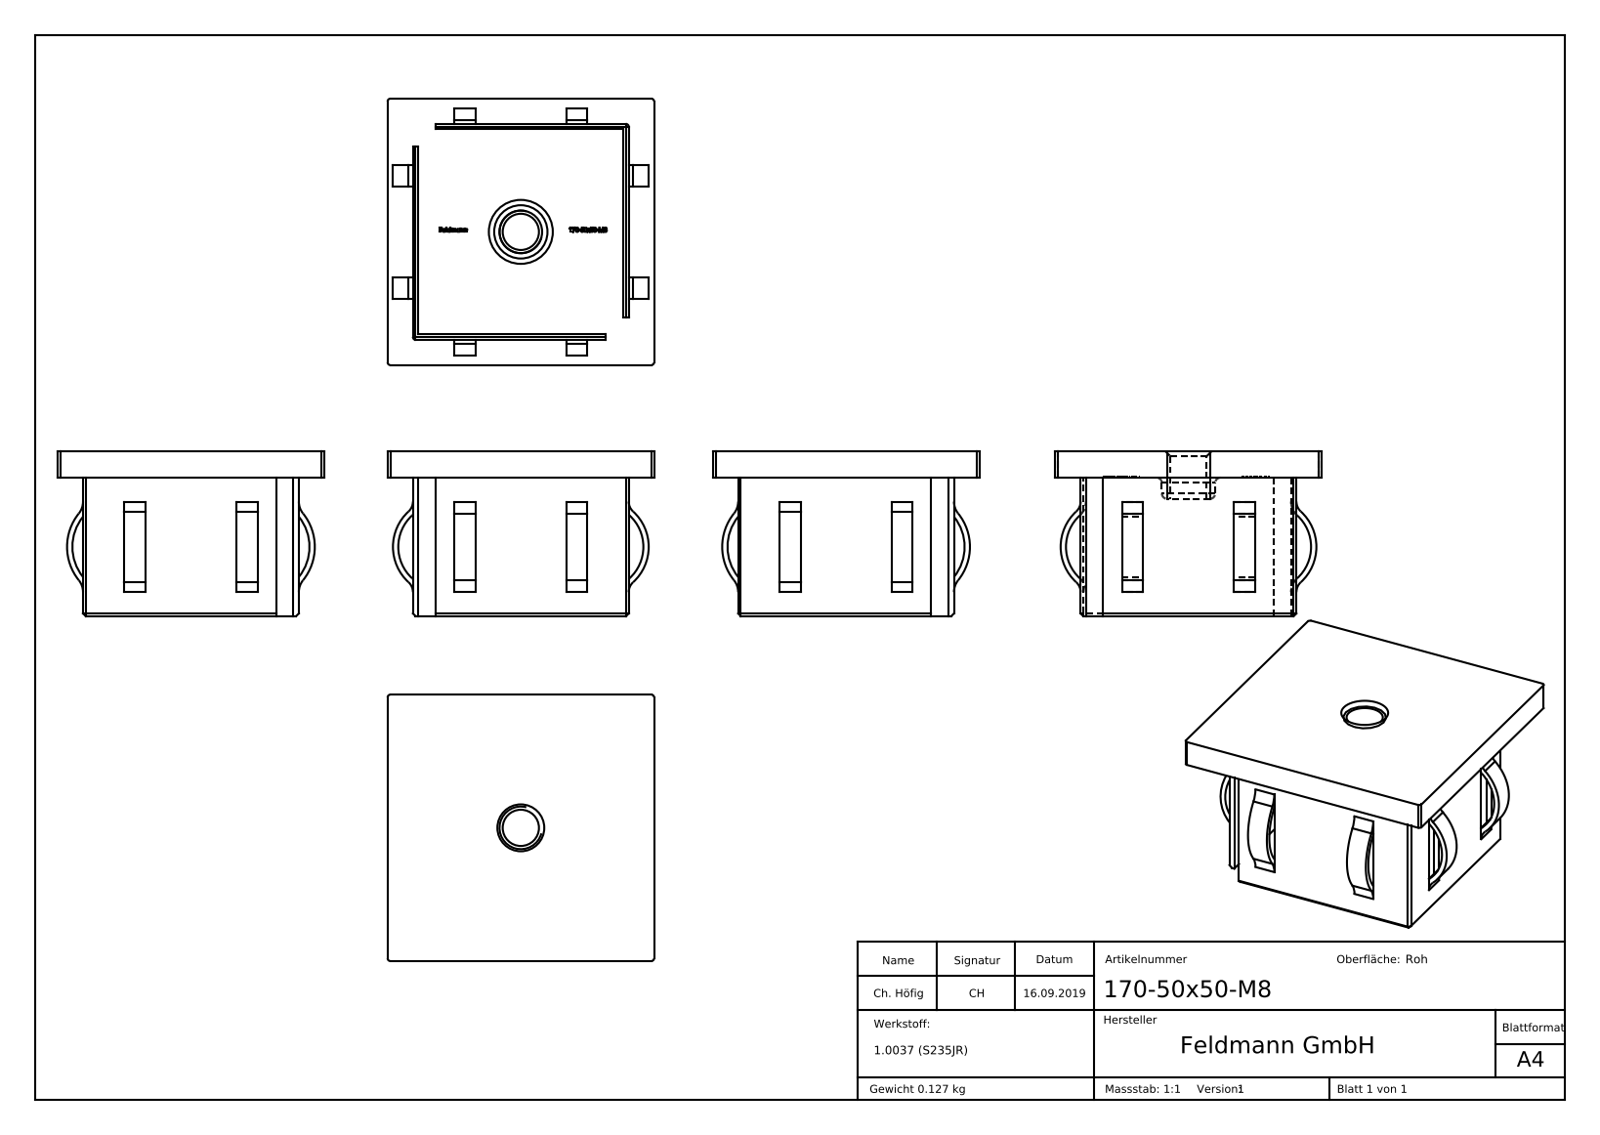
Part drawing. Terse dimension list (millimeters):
name: 170-50x50-M8
written by: SolidWorks 2015 (CONFIG_CONTROL_DESIGN)
unit: mm
bodies: 1 solid, 406 faces (229 planar, 66 cylindrical, 111 other)
size: 50 × 50 × 31
volume: 16 228 mm³; area: 14 264 mm²
holes: 1× ⌀6.8
bosses: 1× ⌀10
rounds: 6× R0.5, 4× R2.51, 4× R3.51, 4× R3.54, 4× R4.54, 4× R9, 2× R8, 2× R10
face distances: 1, 39.5, 5, 38.5, 40.5, 4.75, 5.75, 44.25, 45.25, 50
